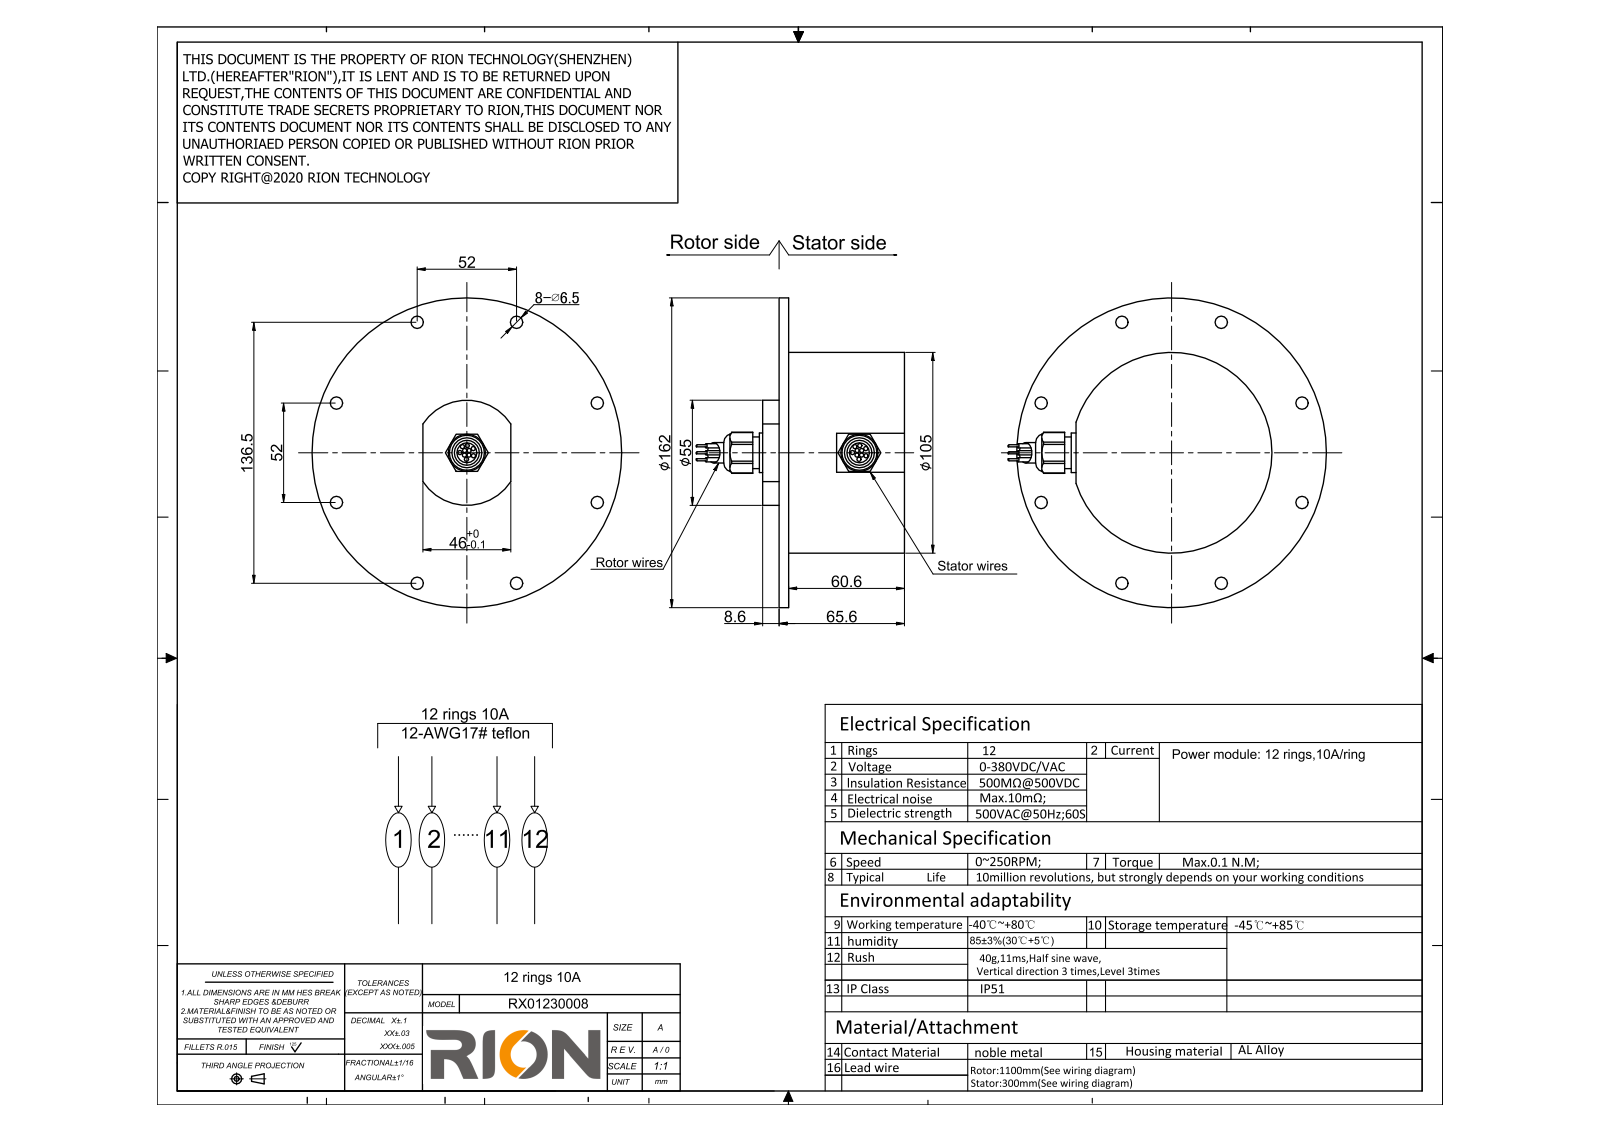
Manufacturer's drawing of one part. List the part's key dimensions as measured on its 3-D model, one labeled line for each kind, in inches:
STEP written by: SolidWorks 2014 (CONFIG_CONTROL_DESIGN)
Units: inches
Bodies: 1 solid, 82 faces (24 planar, 34 cylindrical, 24 other)
Overall size (bounding box): 6.779 × 6.378 × 4.511
Volume: 39.91 in³ · Surface area: 110.4 in²
Round holes (diameter × count): ⌀0.256 ×8, ⌀0.765 ×1
Round bosses / shafts (diameter × count): ⌀0.315 ×2, ⌀0.833 ×1, ⌀0.815 ×1, ⌀0.815 ×1, ⌀0.652 ×1, ⌀0.652 ×1
Partial cylindrical surfaces — rounded edges, fillets, slot ends (radius × count): R1.083 ×1
Main face-to-face distances: 0.197, 2.583, 2.386, 0.339, 0.535, 2.921, 0.815, 1.063, 1.811, 2.874
Hole centre spacings: 2.875, 4.067, 2.047, 2.352, 5.248, 5.374, 5.751
